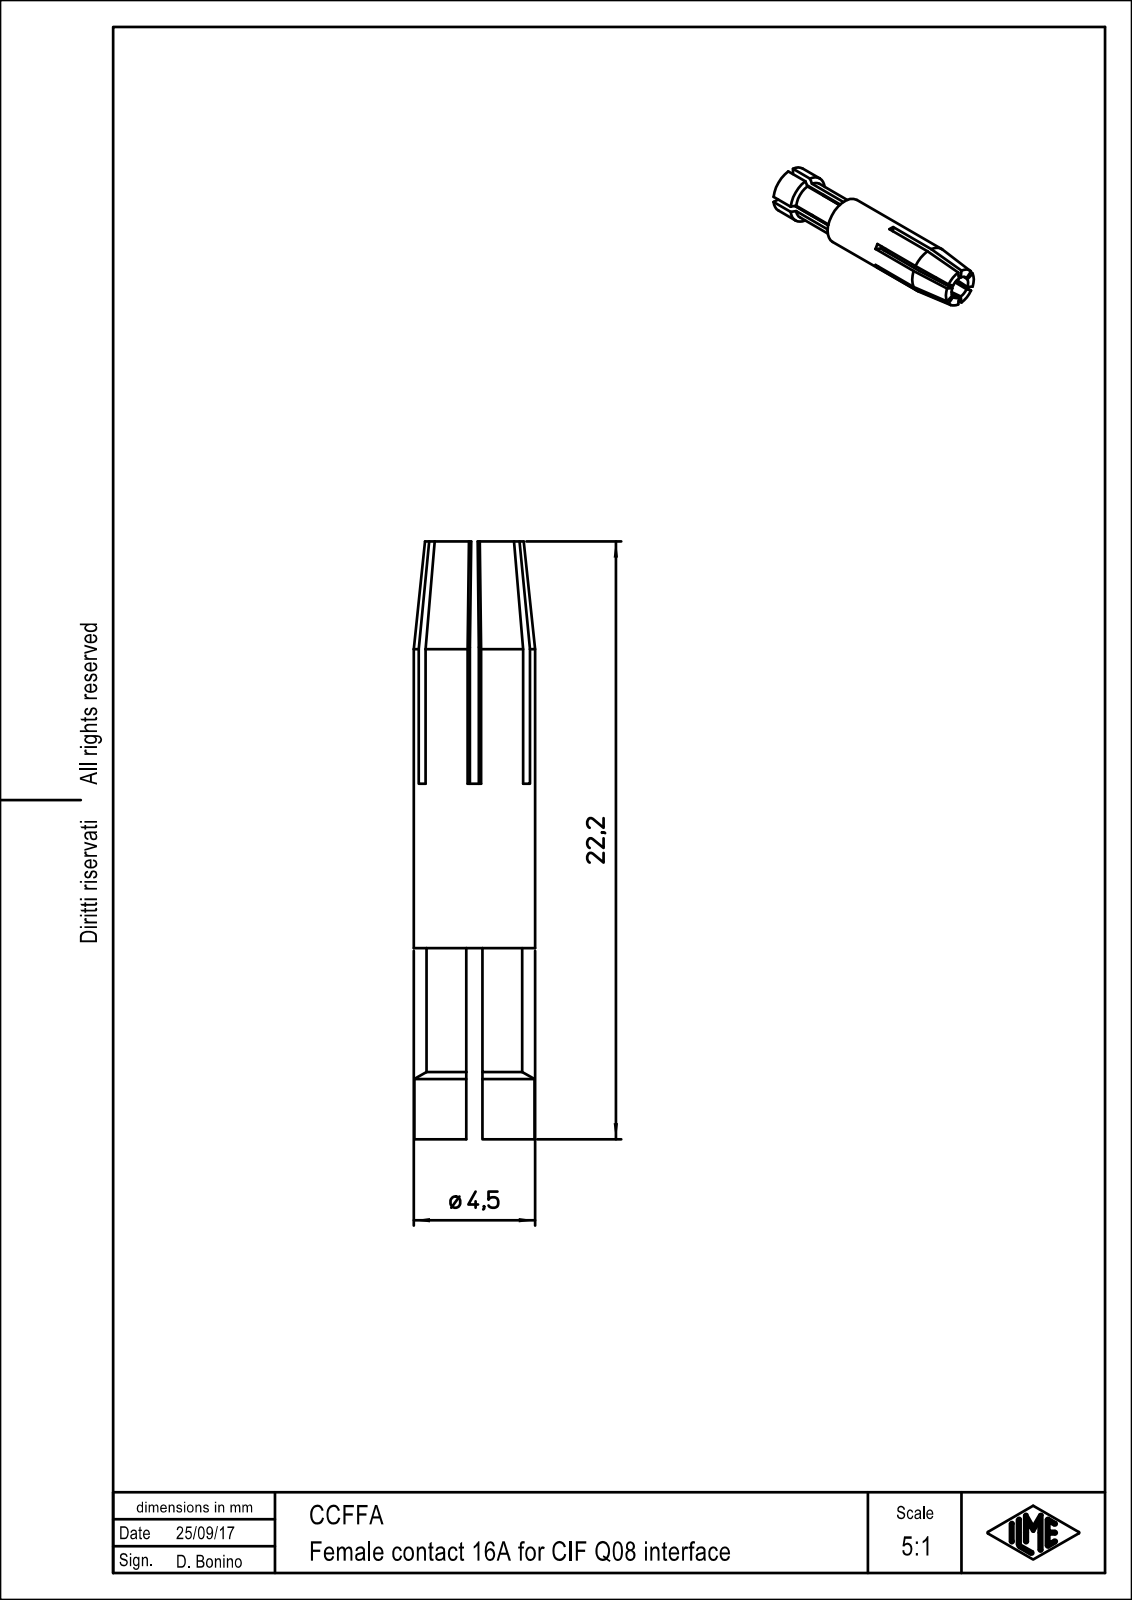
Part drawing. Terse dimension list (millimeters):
name: CCFFA
written by: PTC Creo Elements/Direct Modeling 19.0B 21-Mar-2015 (C) Parametric Technology GmbH (AUTOMOTIVE_DESIGN)
unit: mm
bodies: 1 solid, 69 faces (39 planar, 14 cylindrical, 16 other)
size: 22.2 × 4.5 × 4.5
volume: 181 mm³; area: 529 mm²
holes: 1× ⌀2.6, 1× ⌀3
bosses: 1× ⌀4.5
rounds: 1× R1.8
face distances: 0.6, 11.7, 7.1, 4.6, 22.2, 15.1, 10.5, 7.5, 0.4, 4.2
